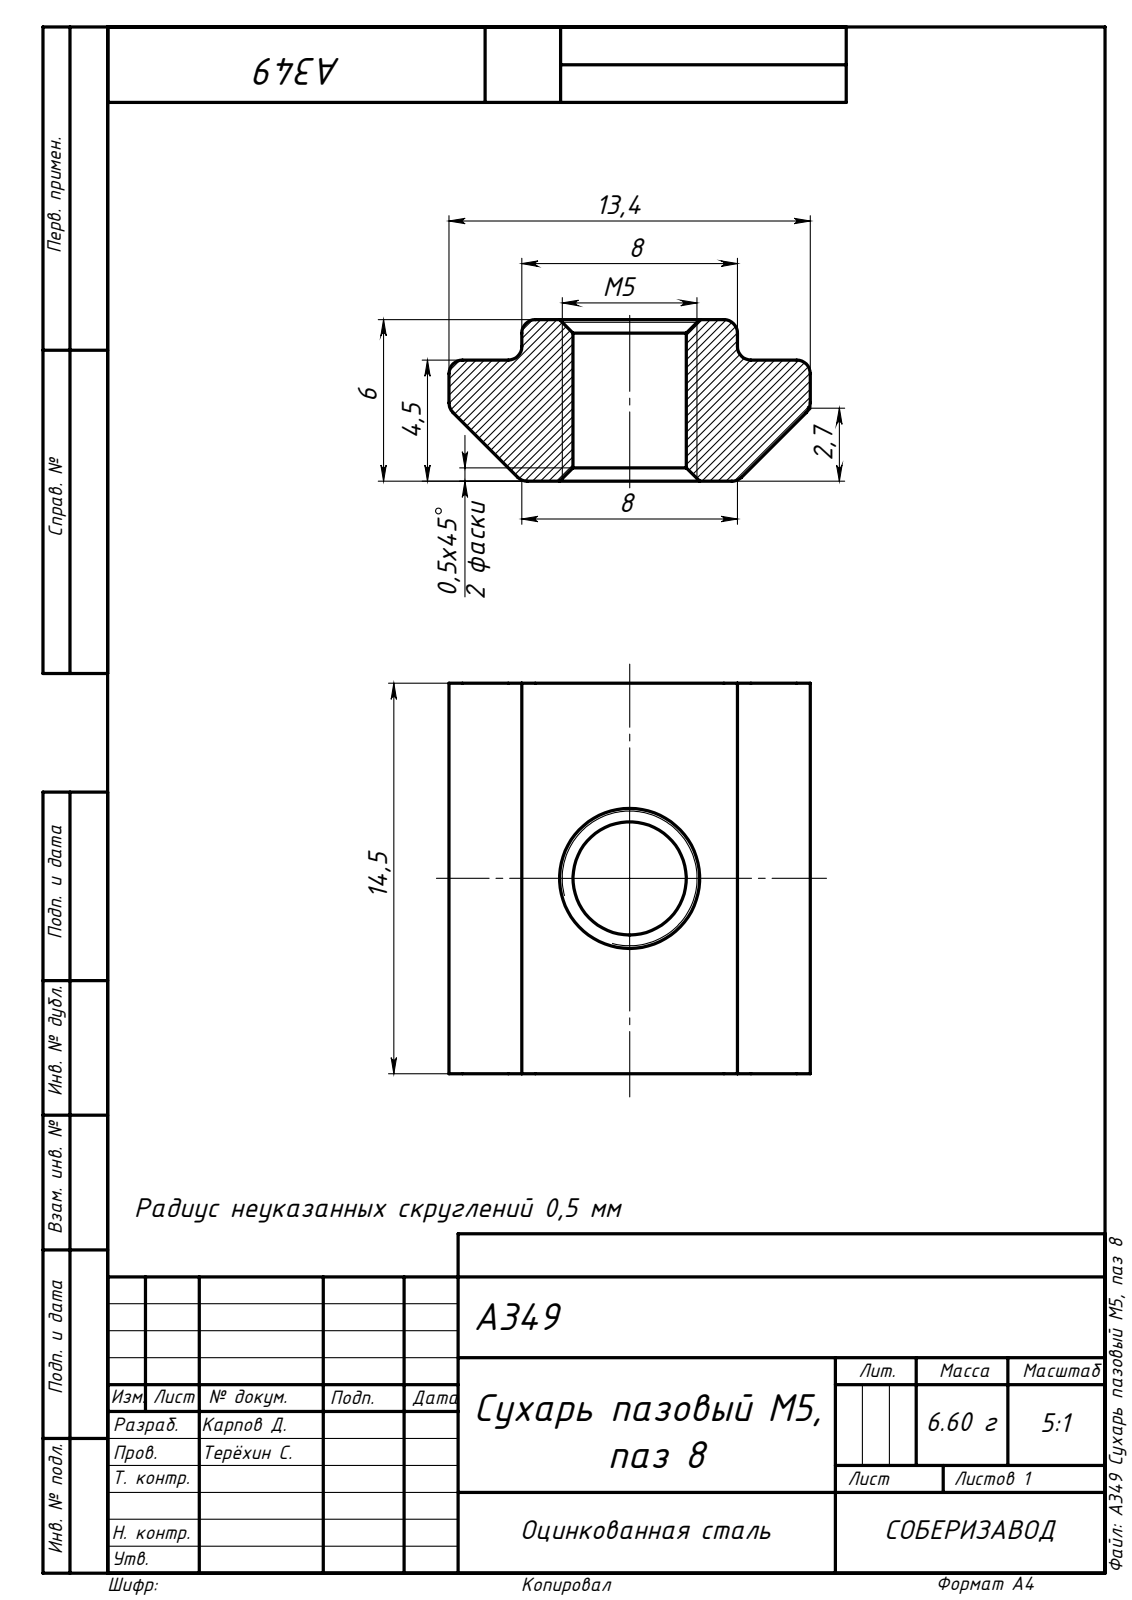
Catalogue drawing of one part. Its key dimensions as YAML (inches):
part_name: "A349 Сухарь пазовый М5, паз 8"
step_written_by: "SolidWorks 2018 (AUTOMOTIVE_DESIGN)"
units: inches
bodies: {solids: 1, faces: 28, planar: 12, cylindrical: 12, other: 4}
overall_size: [0.571, 0.528, 0.236]
volume: 0.052
surface_area: 1.04
round_holes:
  - {diameter: 0.165, count: 1}
partial_cylinders:
  - {radius: 0.02, count: 10}
face_to_face_distances: [0.236, 0.571, 0.059, 0.177, 0.528, 0.106, 0.421, 0.315]
